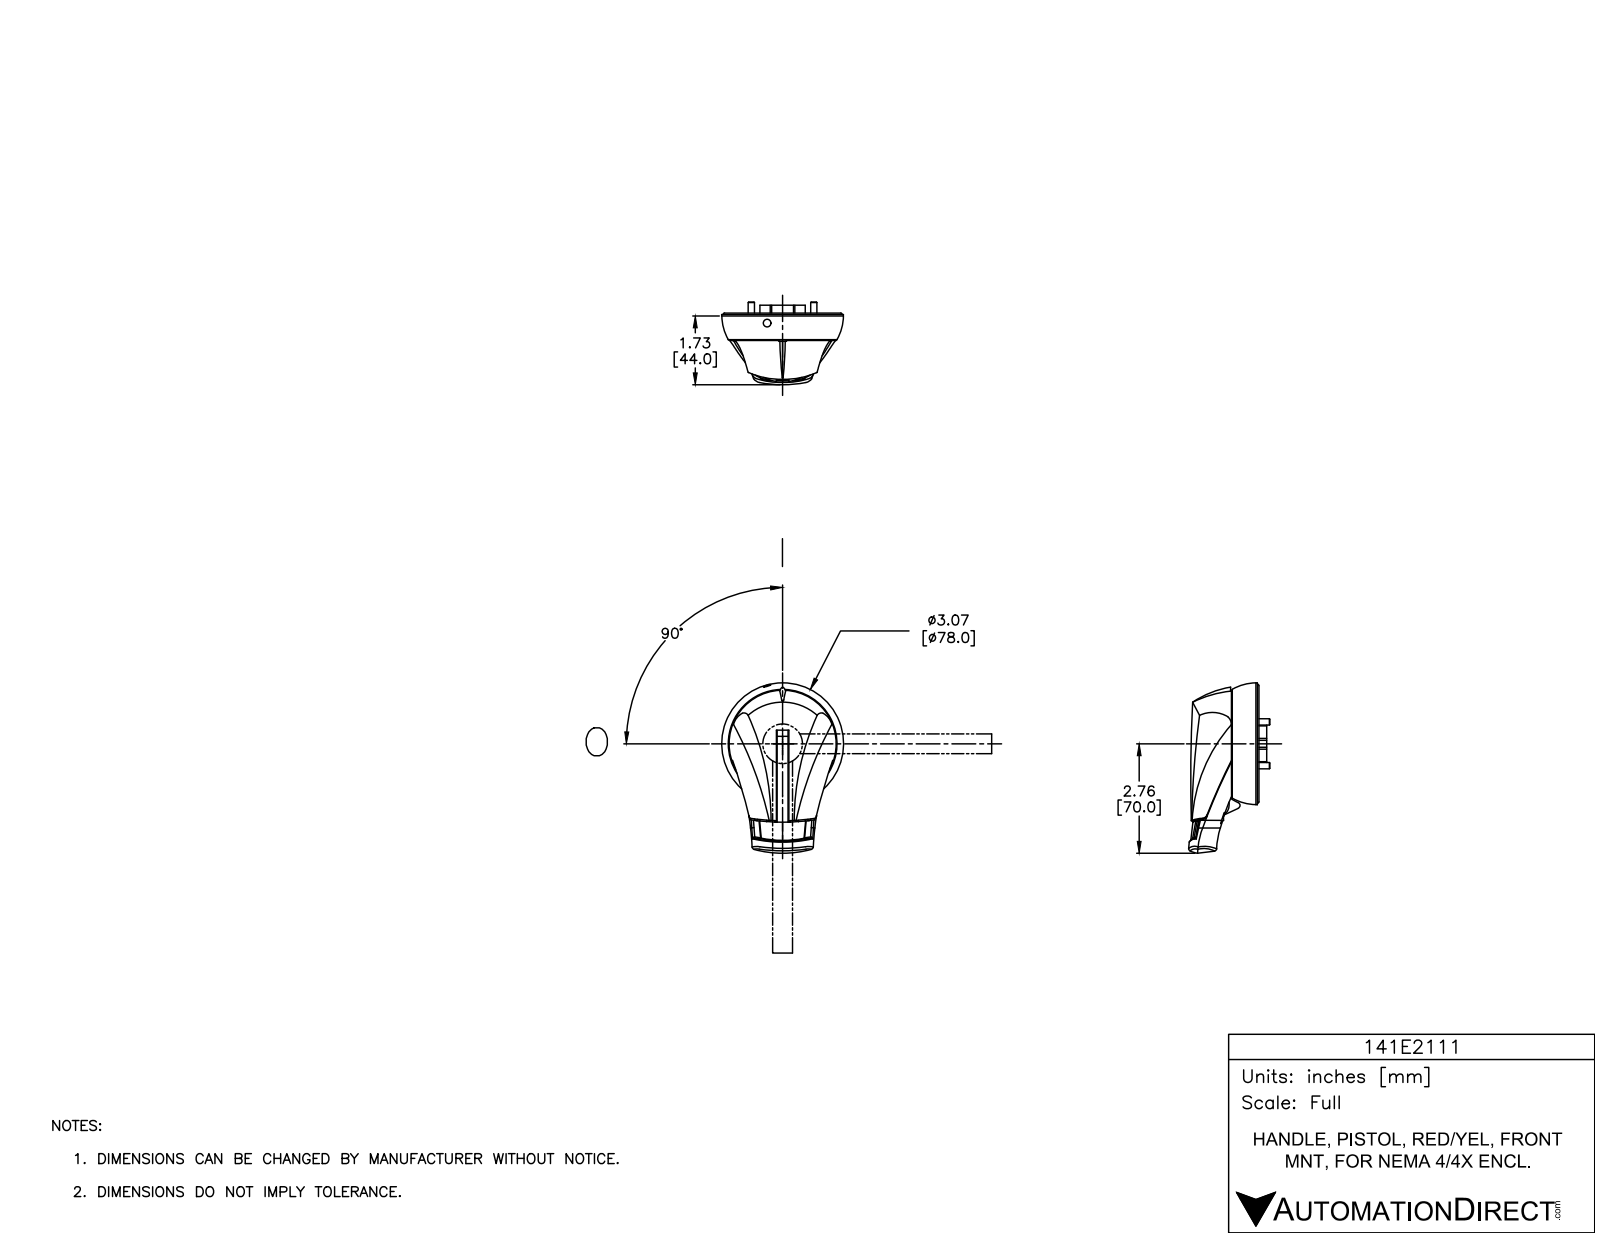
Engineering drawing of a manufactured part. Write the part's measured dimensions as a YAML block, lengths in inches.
part_name: "141E2111"
step_written_by: "SolidWorks 2015 (AUTOMOTIVE_DESIGN)"
units: inches
bodies: {solids: 8, faces: 1516, planar: 810, cylindrical: 548, other: 158}
overall_size: [4.291, 3.07, 2.046]
volume: 7.72
surface_area: 79.65
round_holes:
  - {diameter: 0.157, count: 6}
  - {diameter: 0.339, count: 4}
  - {diameter: 0.425, count: 4}
  - {diameter: 0.03, count: 3}
  - {diameter: 0.169, count: 2}
  - {diameter: 0.362, count: 2}
  - {diameter: 0.118, count: 1}
  - {diameter: 0.189, count: 1}
  - {diameter: 2.992, count: 1}
round_bosses_or_shafts:
  - {diameter: 0.02, count: 11}
  - {diameter: 0.335, count: 4}
  - {diameter: 0.315, count: 4}
  - {diameter: 0.089, count: 3}
  - {diameter: 0.069, count: 3}
  - {diameter: 0.228, count: 2}
  - {diameter: 2.819, count: 1}
  - {diameter: 2.701, count: 1}
partial_cylinders:
  - {radius: 0.01, count: 221}
  - {radius: 0.015, count: 20}
  - {radius: 0.034, count: 20}
  - {radius: 0.03, count: 15}
  - {radius: 0.039, count: 4}
  - {radius: 0.025, count: 3}
  - {radius: 5.437, count: 3}
  - {radius: 0.079, count: 2}
face_to_face_distances: [0.024, 0.701, 0.713, 0.689, 0.035, 0.102, 0.276, 0.173, 0.244, 0.047]
hole_center_spacings: [0.961, 0.309, 0.669, 1.098, 1.102, 1.203, 1.575, 1.881]
